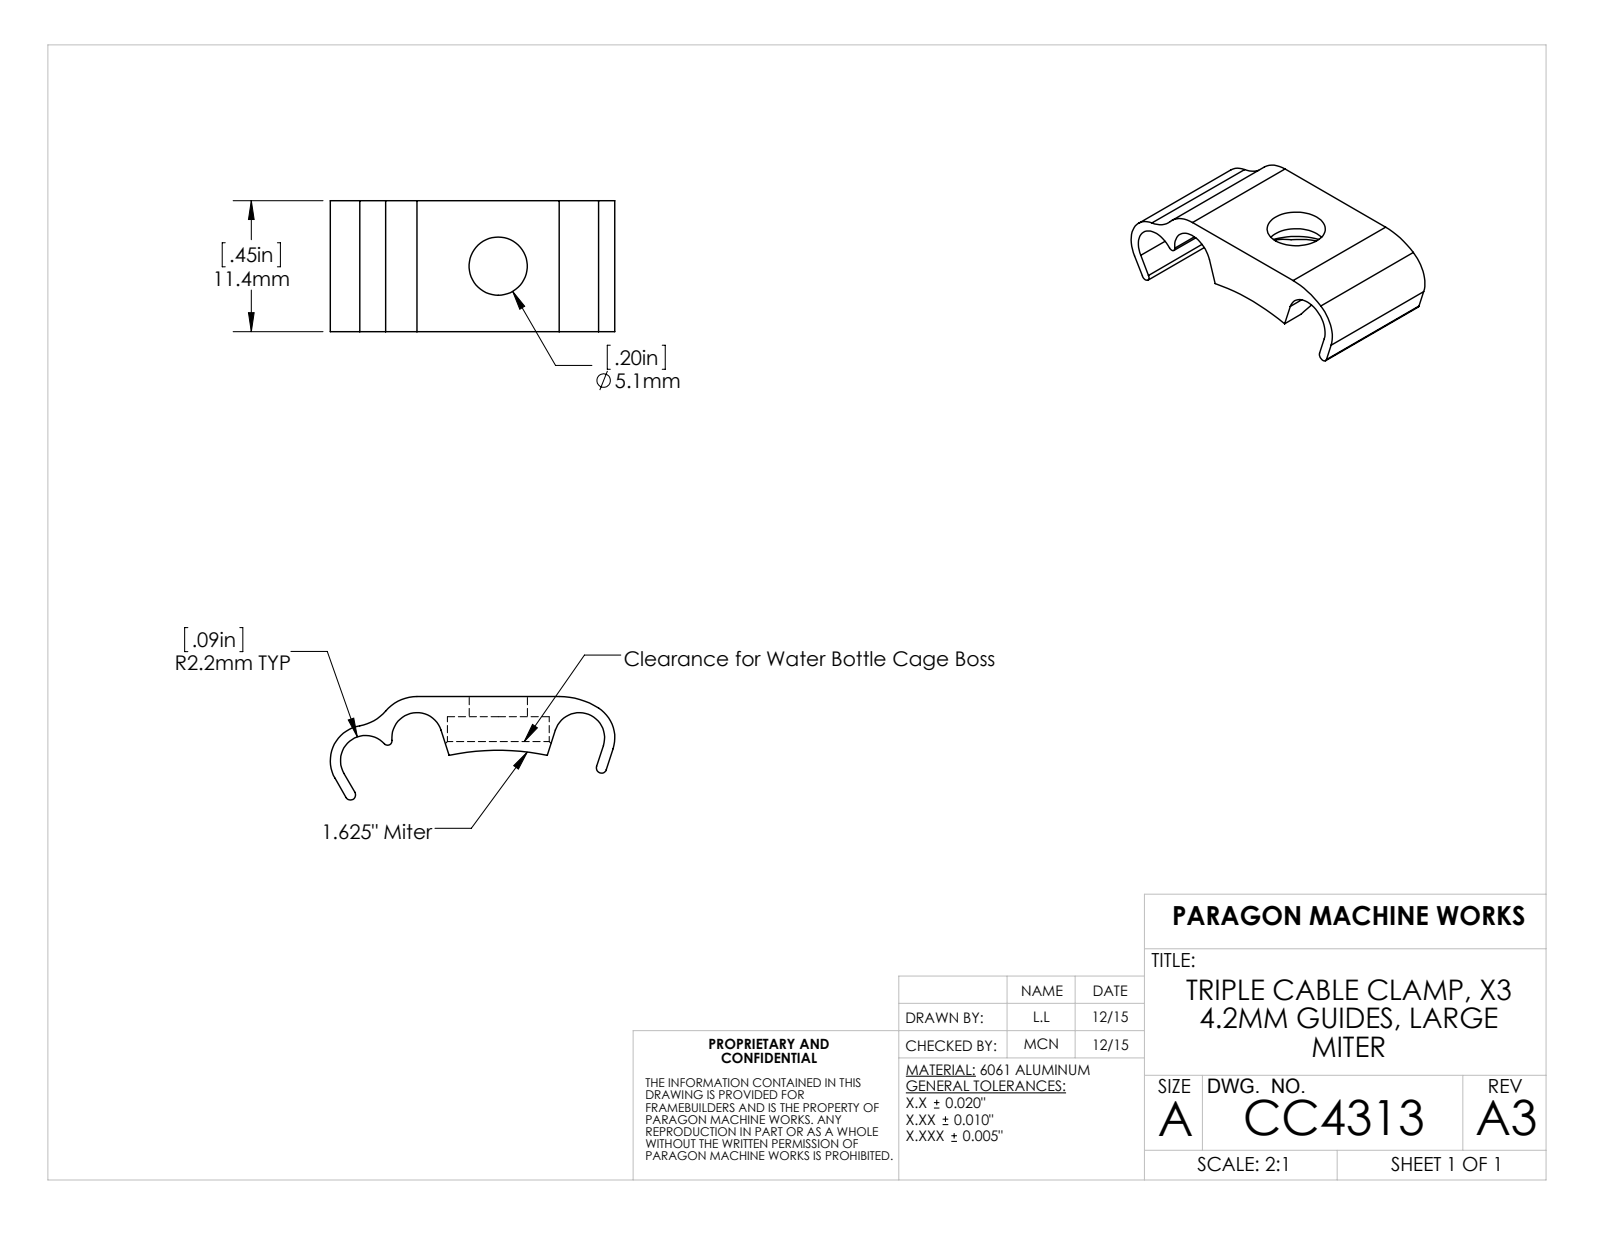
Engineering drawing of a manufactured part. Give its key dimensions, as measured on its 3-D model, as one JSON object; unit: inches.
{"part_name": "CC4313", "step_written_by": "SolidWorks 2015 (AUTOMOTIVE_DESIGN)", "units": "inches", "bodies": {"solids": 1, "faces": 33, "planar": 10, "cylindrical": 21, "other": 2}, "overall_size": [0.978, 0.45, 0.355], "volume_in3": 0.039, "surface_area_in2": 1.666, "round_holes": [[0.2, 1], [0.35, 1]], "partial_cylinders_radius": [[0.087, 3], [0.122, 2], [0.015, 1], [0.017, 1], [0.018, 1], [0.142, 1], [0.15, 1], [0.25, 1]], "face_to_face_distances": [0.45, 0.035, 0.07, 0.173, 0.208]}
